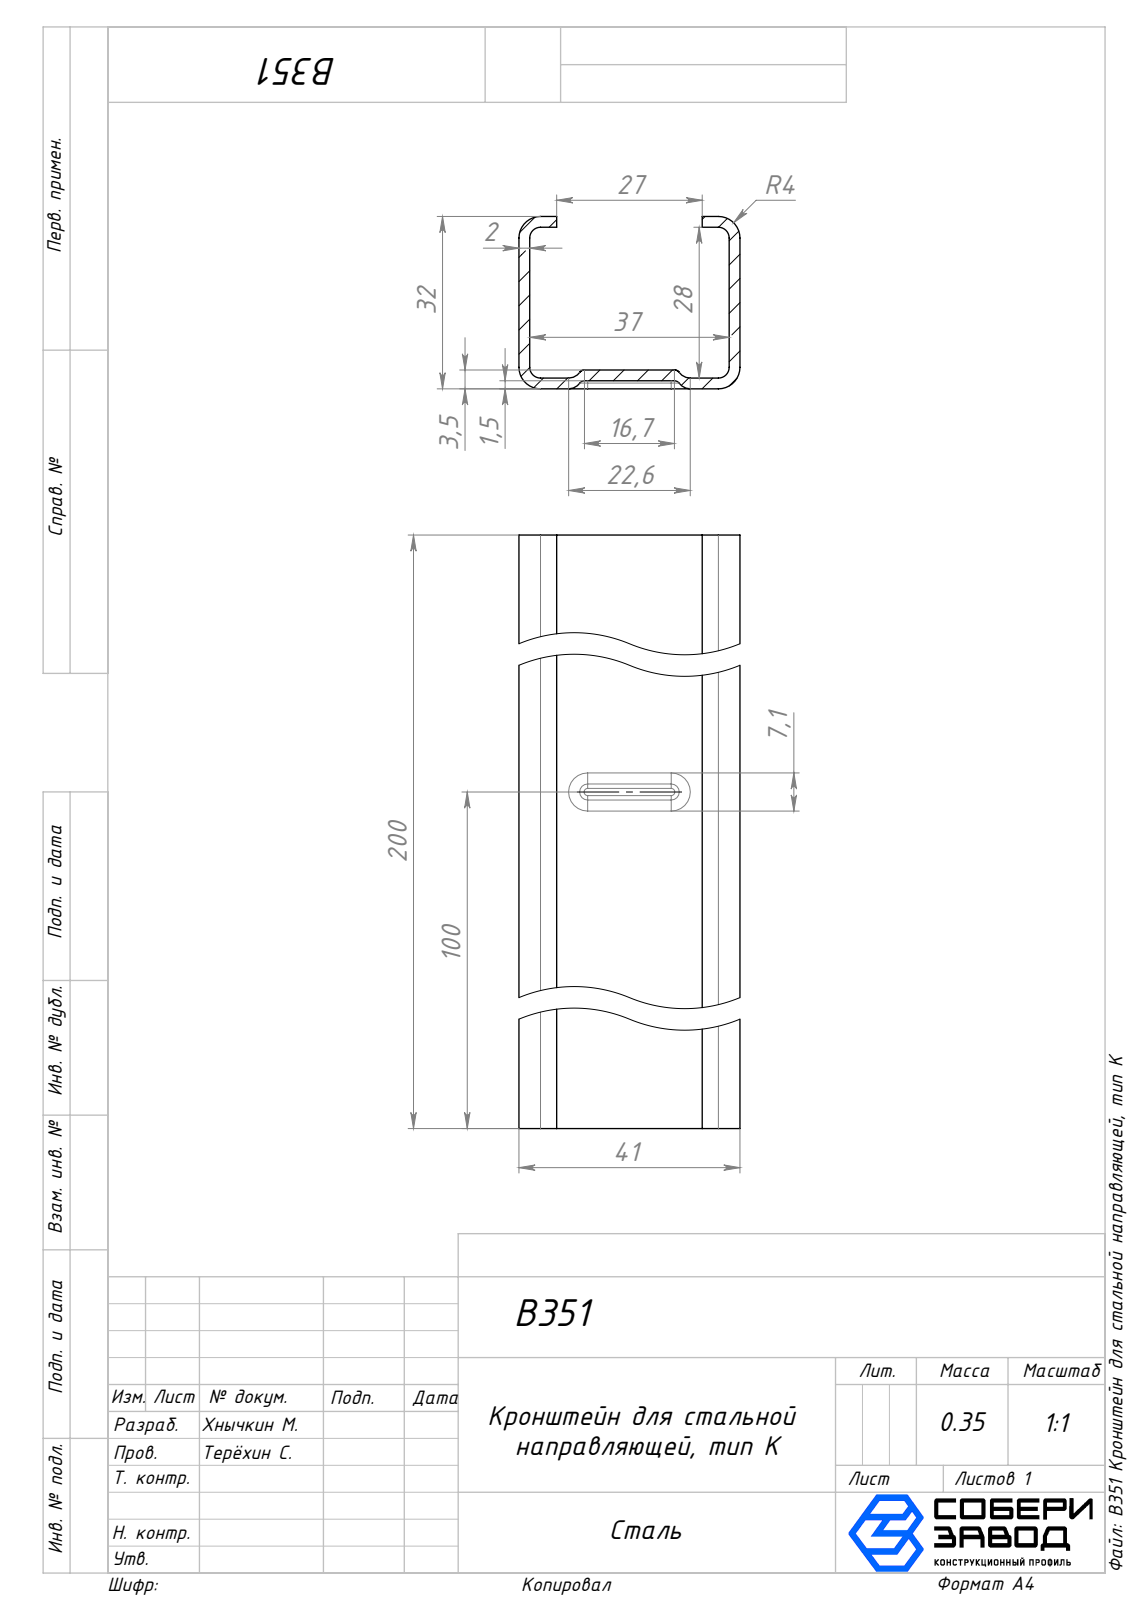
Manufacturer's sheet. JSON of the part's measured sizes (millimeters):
{"part_name": "B351 Кронштейн для стальной направляющей, тип K", "step_written_by": "SolidWorks 2025 (AUTOMOTIVE_DESIGN)", "units": "millimeters", "bodies": {"solids": 1, "faces": 44, "planar": 16, "cylindrical": 16, "other": 12}, "overall_size": [200, 41, 32], "volume_mm3": 42340, "surface_area_mm2": 43605, "partial_cylinders_radius": [[1, 4], [2, 4], [2.5, 4], [4, 4]], "face_to_face_distances": [2, 39, 41, 37, 30, 32, 28, 7, 34, 5]}
